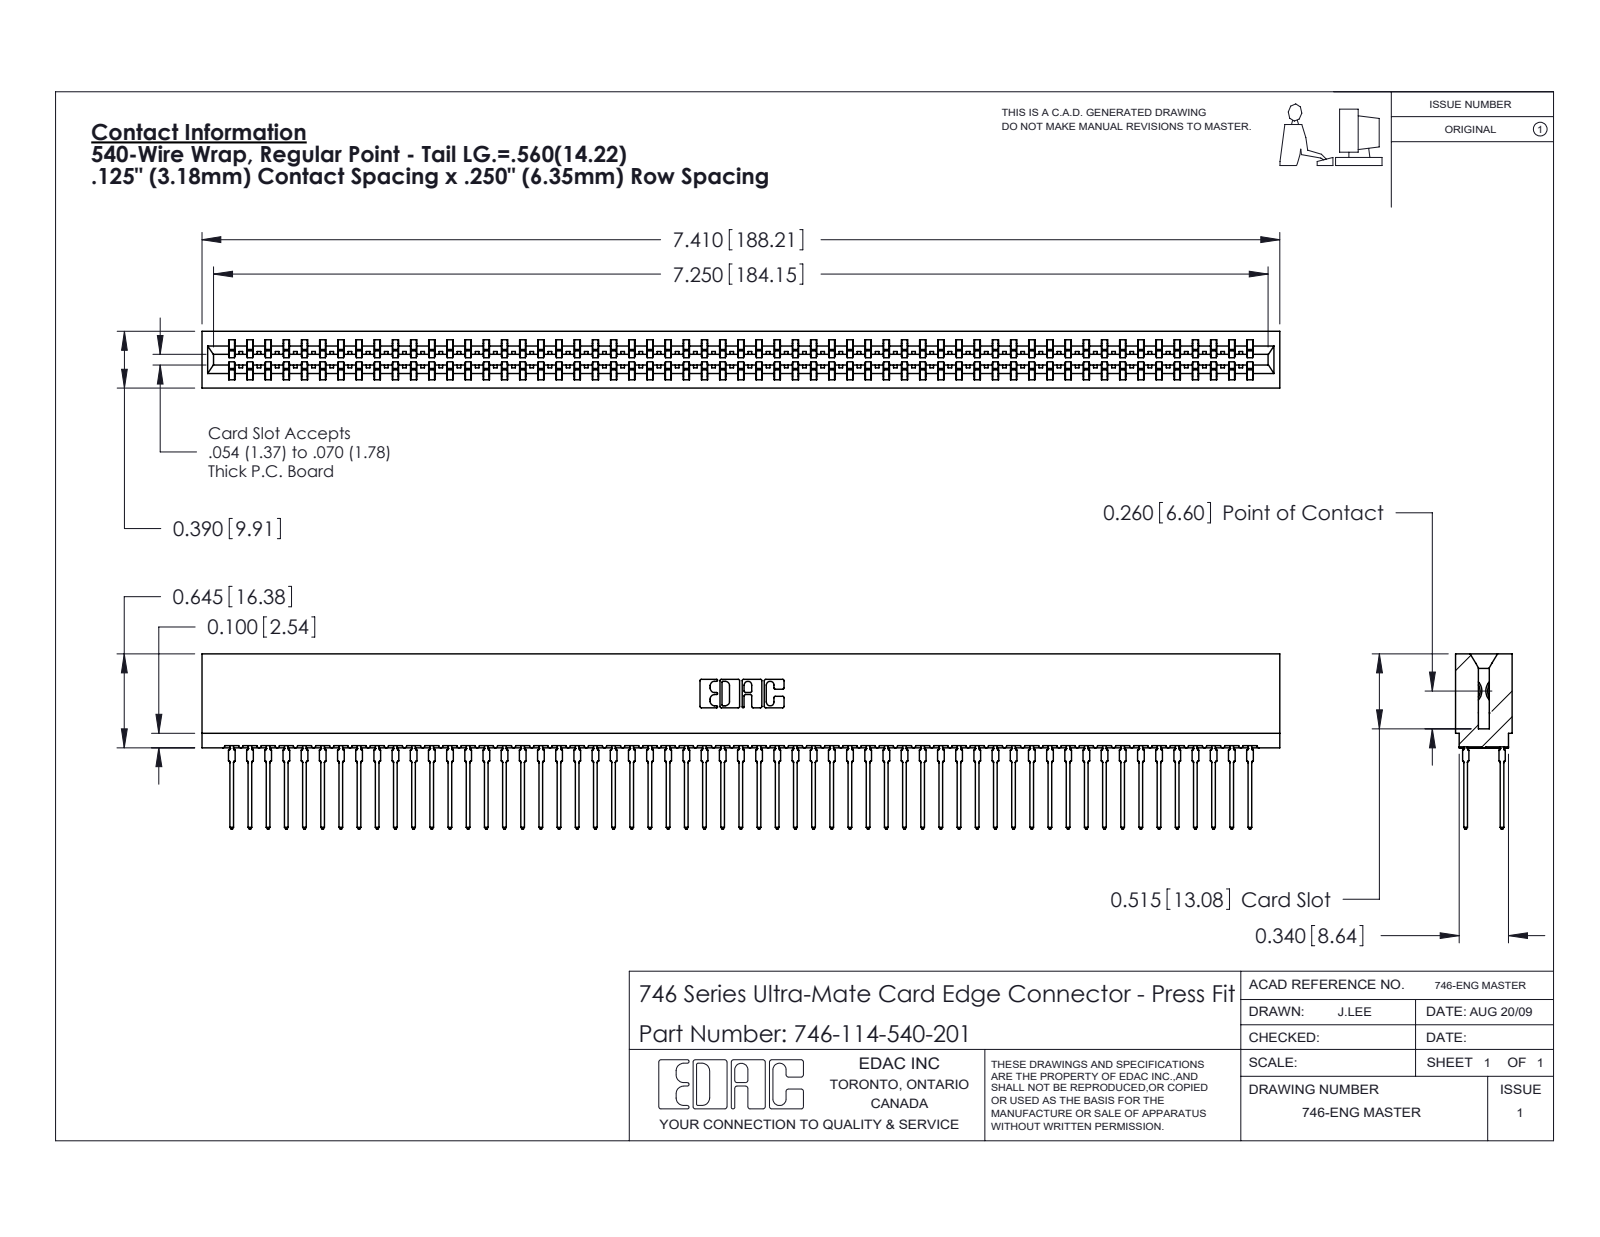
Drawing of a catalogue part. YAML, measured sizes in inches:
part_name: "746-292-001_540; 746-114-540-201; 746 Part_.515 Slot Depth - 01"
step_written_by: "SolidWorks 2020 (CONFIG_CONTROL_DESIGN)"
units: inches
bodies: {solids: 115, faces: 10300, planar: 5299, cylindrical: 2037, other: 2964}
overall_size: [7.41, 1.204, 0.39]
volume: 1.247
surface_area: 53.78
partial_cylinders:
  - {radius: 0.021, count: 228}
  - {radius: 0.015, count: 58}
  - {radius: 0.01, count: 22}
  - {radius: 0.005, count: 8}
  - {radius: 0.011, count: 8}
  - {radius: 0.007, count: 6}
  - {radius: 0.031, count: 6}
  - {radius: 0.026, count: 3}
face_to_face_distances: [0.057, 0.333, 0.25, 0.39, 0.025, 0.307, 0.083, 0.275, 0.174, 0.158]
